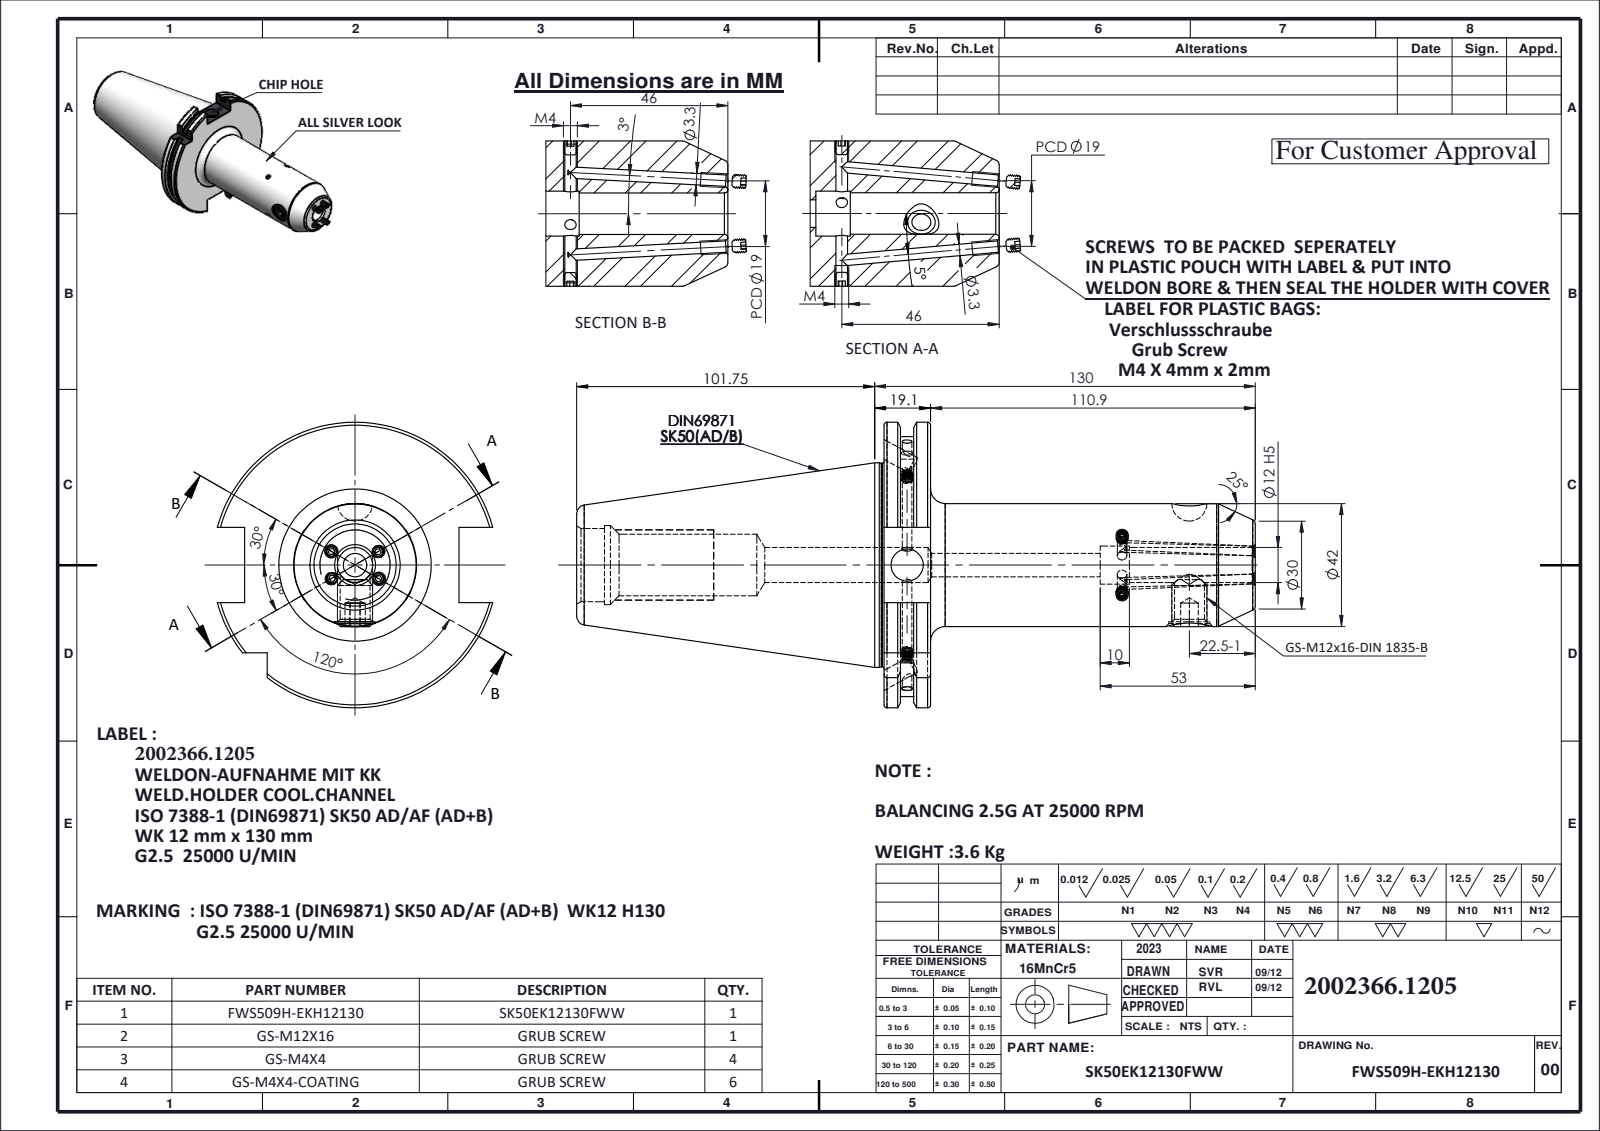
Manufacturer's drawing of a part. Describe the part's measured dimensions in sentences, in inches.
The part is named "GS-M12X16-DIN1835-B; SK50EK12130FWW; FWS509H-EKH12130; GS-M4X4_DIN 913 - M4 x 4-N (+1 more)". Its 3-D file was written by "SolidWorks 2023 (CONFIG_CONTROL_DESIGN)". It is 12 solids with 661 faces: 130 planar, 181 cylindrical and 350 other. Overall it measures 9.367 by 3.839 by 3.703 inches. Its volume is 28.67 cubic inches and its surface area 101.5 square inches. Round holes: 8 of diameter 0.13, 2 of diameter 0.236, 1 of diameter 0.315, 1 of diameter 0.402, 1 of diameter 0.433, 1 of diameter 0.472, 1 of diameter 0.512, 1 of diameter 0.551, 1 of diameter 0.827, 1 of diameter 0.984, 1 of diameter 1.063. Round bosses or shafts: 9 of diameter 0.157, 1 of diameter 2.75, 1 of diameter 2.734, 1 of diameter 1.654, 1 of diameter 0.472. Partial cylindrical surfaces (rounded edges, fillets, slot ends): 1 of radius 1.768, 1 of radius 1.919. The main face-to-face distances are 0.626, 0.222, 0.404, 0.399, 0.177, 0.227, 4.992, 4.77, 4.593, 4.366.
